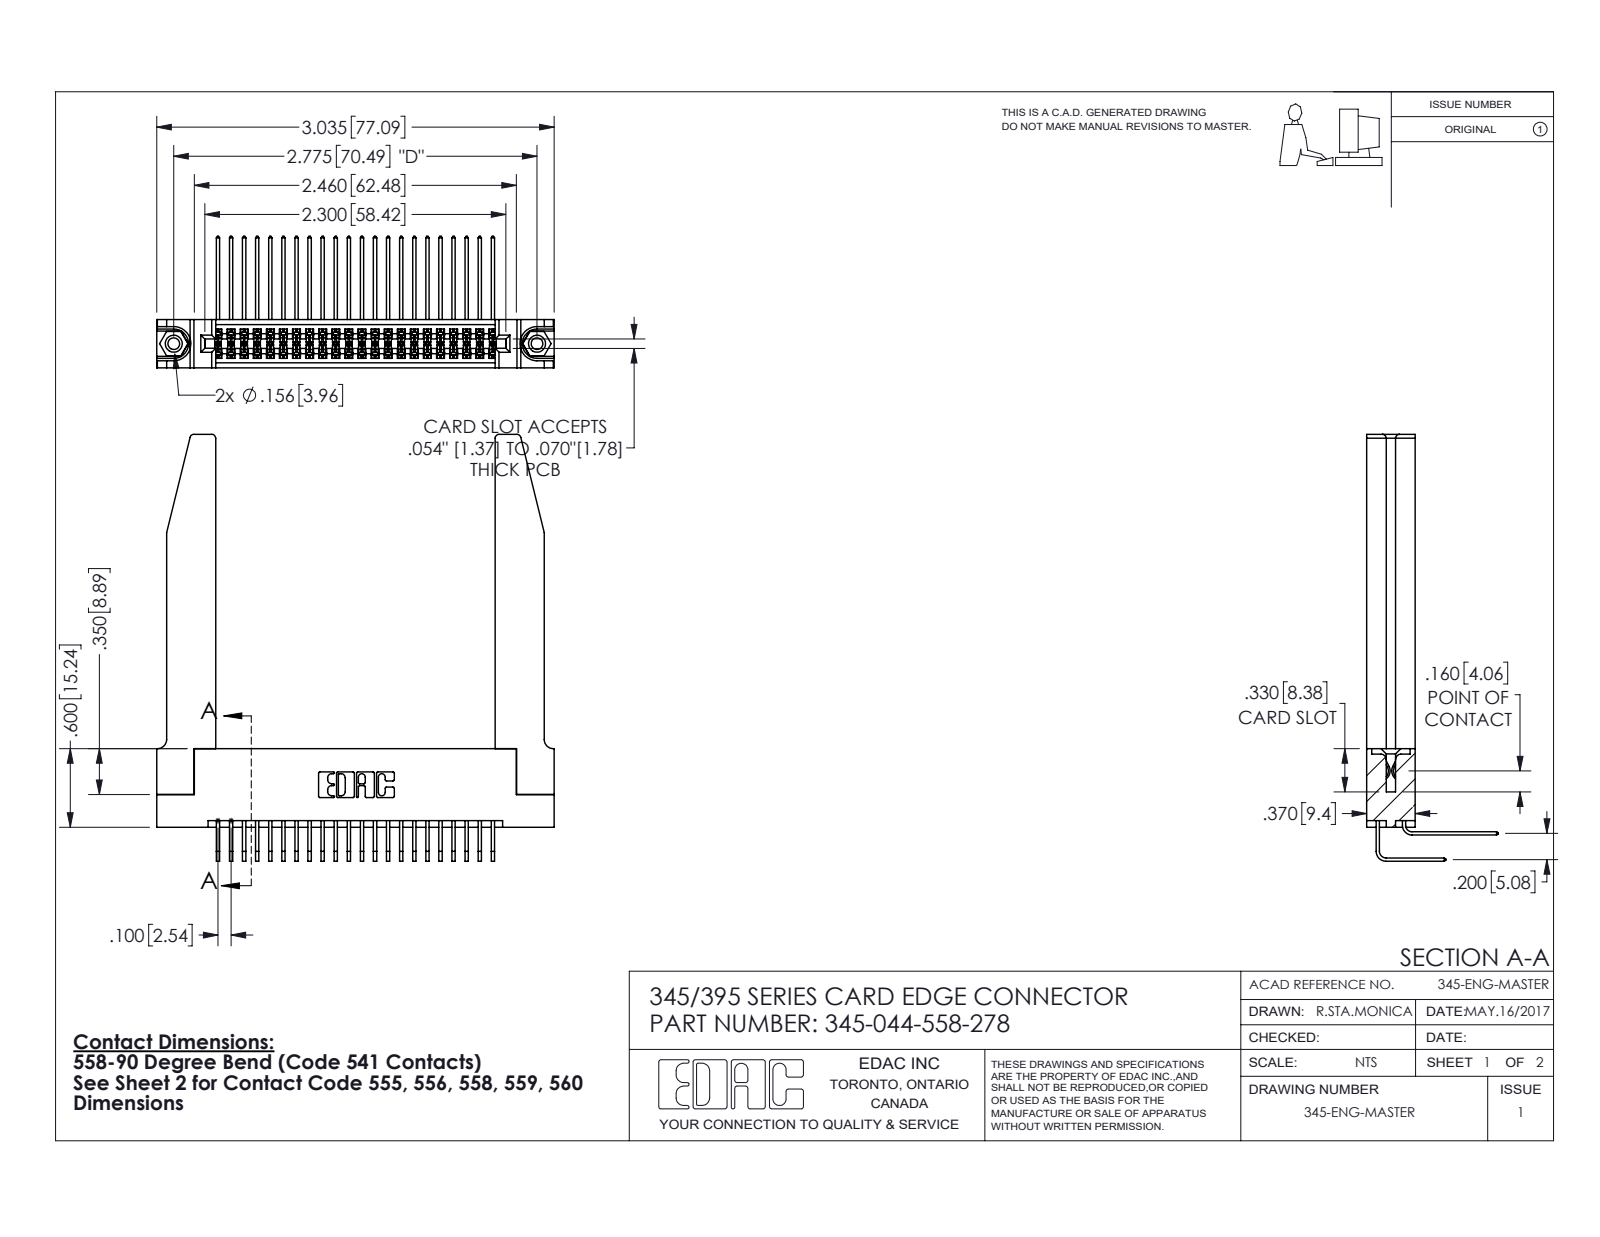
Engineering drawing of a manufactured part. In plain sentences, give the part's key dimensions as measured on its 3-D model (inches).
The part is named "345-250-001_345-250-001-102; 345-044-558-278; 345-292-001_558 559 Tail - 1; 345 Part_Flush Mounting Lugs - 0.156 Dia-TH (+2 more)". Its 3-D file was written by "SolidWorks 2016 (CONFIG_CONTROL_DESIGN)". It is 49 solids with 2648 faces: 1762 planar, 834 cylindrical and 52 other. Overall it measures 3.259 by 3.036 by 1.005 inches. Its volume is 0.935 cubic inches and its surface area 29.17 square inches. Round holes: 2 of diameter 0.089, 2 of diameter 0.125, 2 of diameter 0.156, 1 of diameter 0.064. Round bosses or shafts: 2 of diameter 0.155. Partial cylindrical surfaces (rounded edges, fillets, slot ends): 88 of radius 0.006, 22 of radius 0.01, 8 of radius 0.03, 6 of radius 0.007, 6 of radius 0.031, 3 of radius 0.026, 2 of radius 0.014, 2 of radius 0.019. The main face-to-face distances are 0.37, 0.072, 0.298, 0.2, 0.098, 0.272, 0.025, 0.225, 0.148, 0.15. The hole center spacings are 0.27, 2.541, 2.775.
